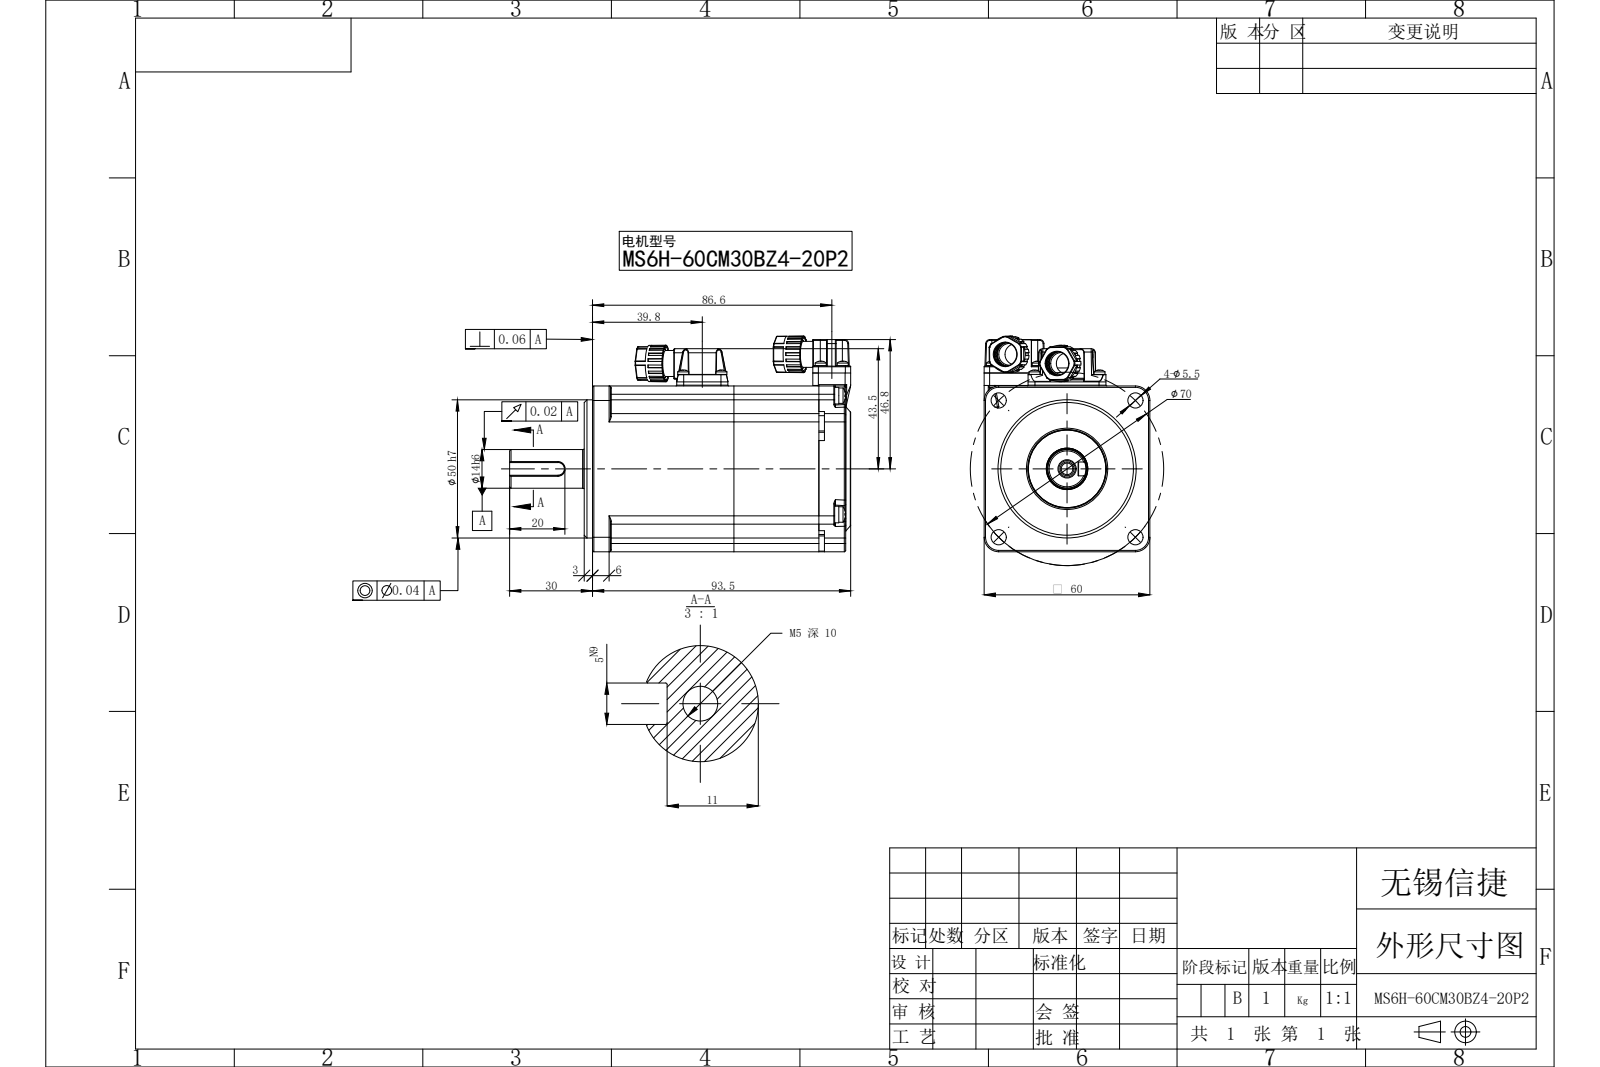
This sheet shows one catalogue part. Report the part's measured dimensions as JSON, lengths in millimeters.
{"part_name": "MS6H-60CM30BZ4-20P2", "step_written_by": "SolidWorks 2022 (CONFIG_CONTROL_DESIGN)", "units": "millimeters", "bodies": {"solids": 0, "faces": 1162, "planar": 468, "cylindrical": 410, "other": 284}, "overall_size": [123.45, 78.06, 60], "round_holes": [[5.5, 4], [11.5, 2], [11.7, 2], [4.2, 1], [5, 1], [10.4, 1], [15, 1]], "round_bosses_or_shafts": [[4, 8], [6, 4], [5.6, 4], [5.5, 4], [9.4, 2], [50, 1], [28, 1], [14, 1]], "partial_cylinders_radius": [[0.5, 50], [0.3, 39], [0.35, 23], [0.2, 22], [3, 17], [1.5, 13], [2, 10], [0.15, 6]], "face_to_face_distances": [60, 11.5, 84.95, 3, 96.45, 93.45, 81.95, 10, 50, 1.8], "hole_center_spacings": [35, 49.5, 29.29, 29.3, 70, 29.31]}
